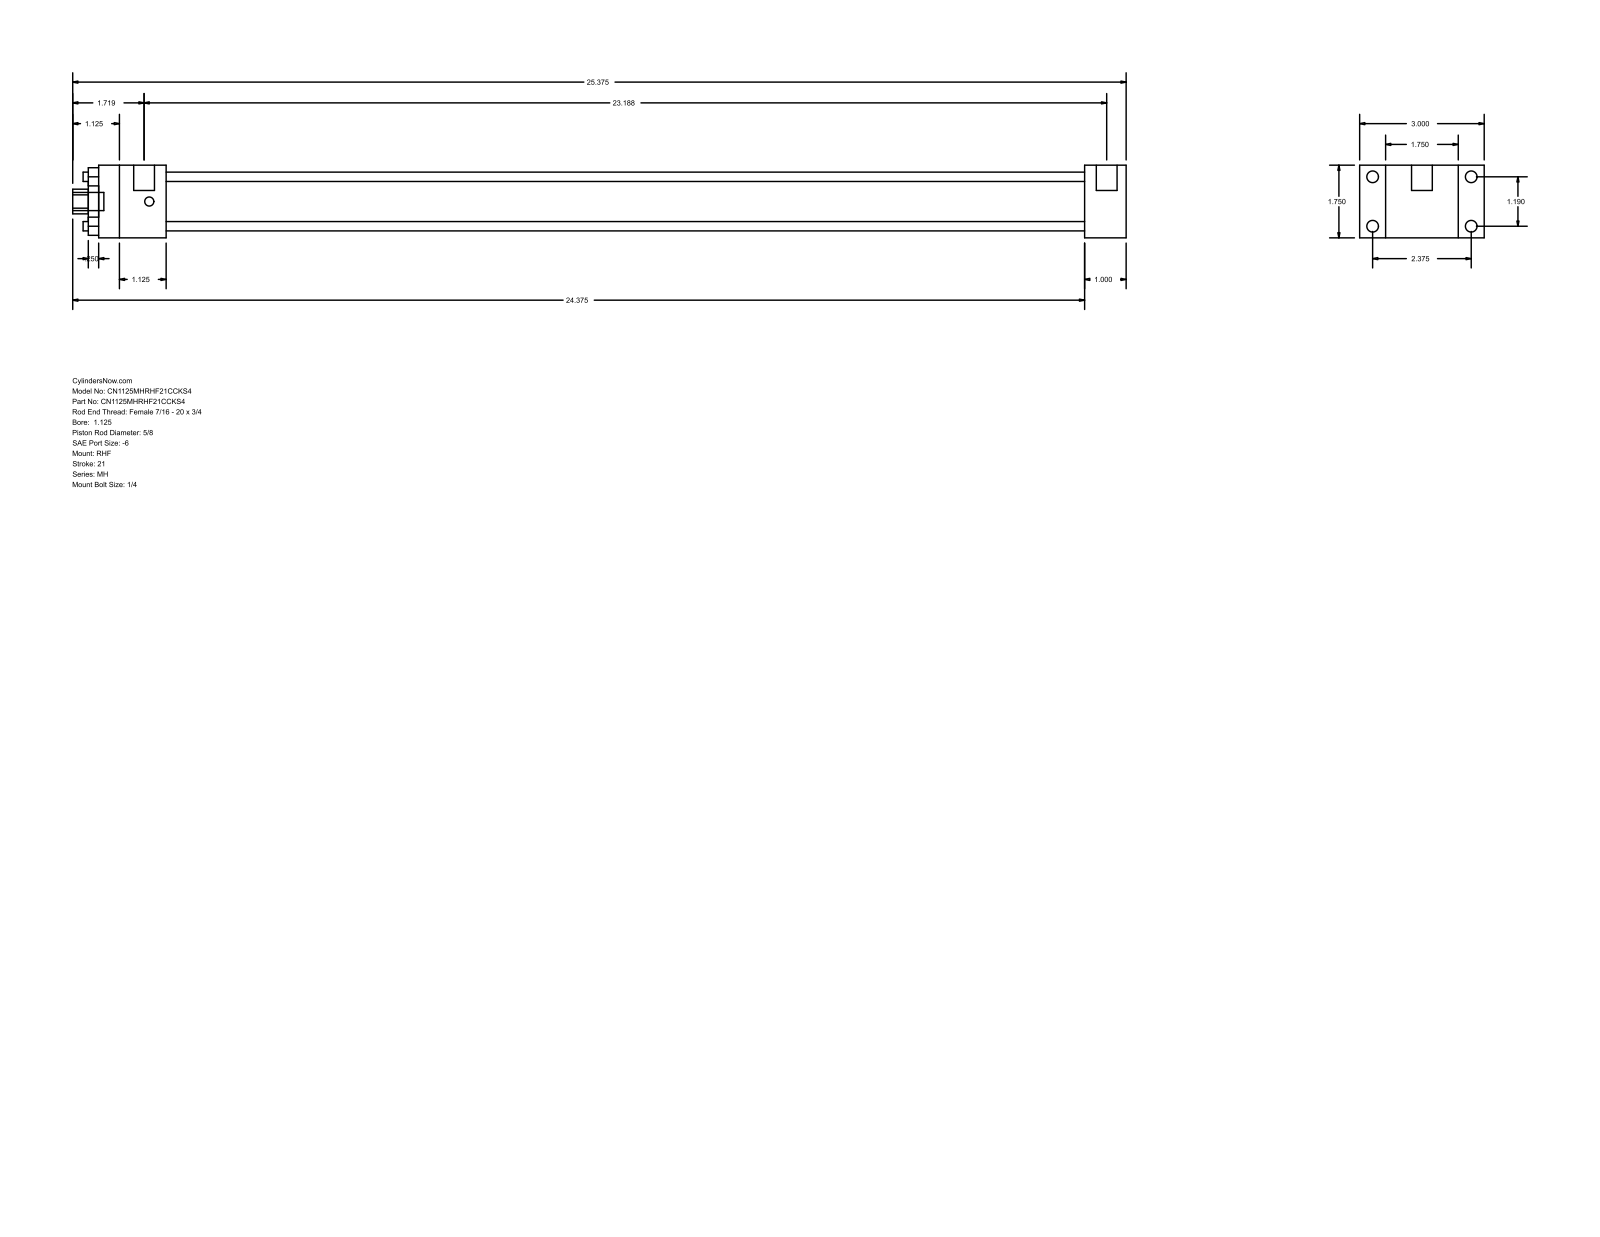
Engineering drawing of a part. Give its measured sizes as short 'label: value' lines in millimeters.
name: MH_RHF__0112_0.625
written by: GSSL Pune (CONFIG_CONTROL_DESIGN)
unit: mm
bodies: 0 solids, 88 faces (60 planar, 28 cylindrical, 0 other)
size: 644.52 × 76.2 × 44.45
holes: 4× ⌀5.71, 1× ⌀15.88, 1× ⌀28.57, 1× ⌀34.92
bosses: 4× ⌀7.14, 4× ⌀5.56, 2× ⌀12.7, 1× ⌀11.11
rounds: 1× R7.54
face distances: 44.46, 15.87, 60.33, 25.4, 76.2, 561.97, 587.37, 41.27, 603.24, 628.64
hole spacings: 21.37, 30.22, 42.74
